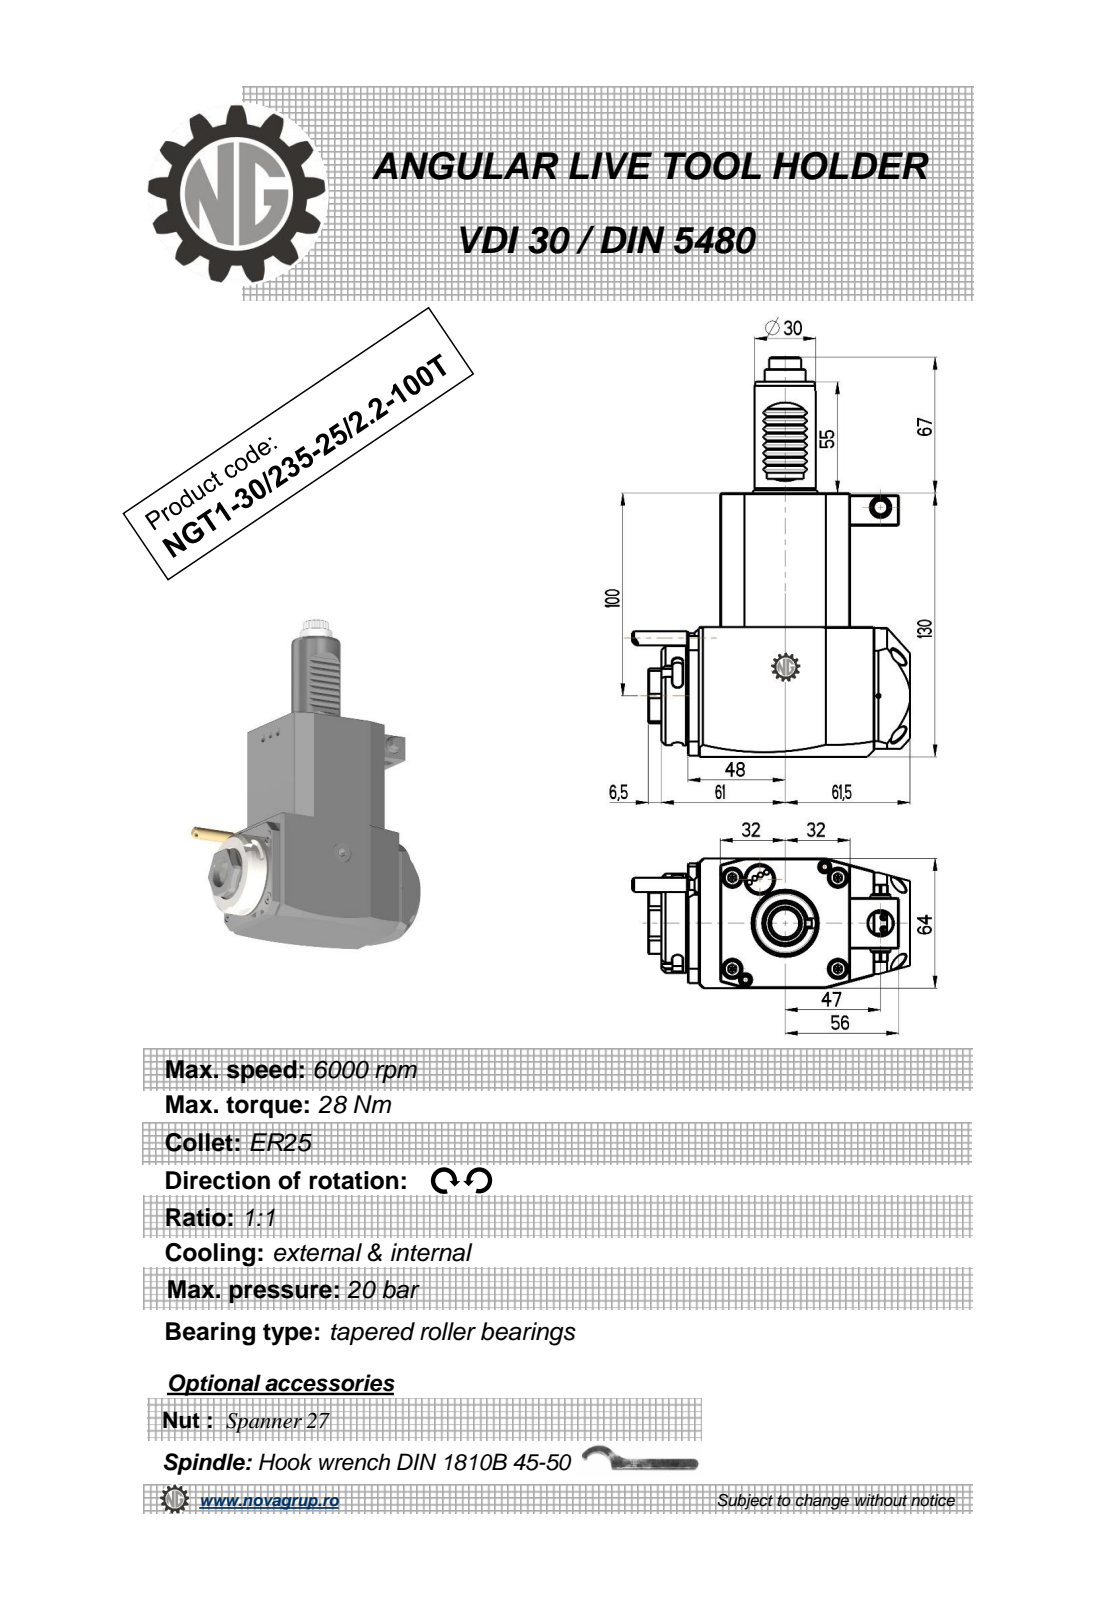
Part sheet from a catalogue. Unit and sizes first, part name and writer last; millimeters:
Units: millimetres
Overall size (bounding box): 197 × 136.88 × 64
Round holes (diameter × count): ⌀2.5 ×1, ⌀3 ×1, ⌀9.5 ×1, ⌀12 ×1, ⌀18 ×1
Round bosses / shafts (diameter × count): ⌀8 ×2, ⌀49 ×1, ⌀42 ×1, ⌀30 ×1, ⌀20 ×1, ⌀10 ×1, ⌀7 ×1, ⌀5 ×1
Partial cylindrical surfaces — rounded edges, fillets, slot ends (radius × count): R1.98 ×36, R0.3 ×8, R2.5 ×6, R180 ×2, R3.85 ×1, R4.25 ×1, R4.5 ×1, R7.08 ×1
Main face-to-face distances: 64, 130, 16, 80, 72.18, 13, 29.5, 93.5, 109.5, 66
Hole centre spacings: 34.25, 65.8, 91.5
Volume: 739 925 mm³ · Surface area: 62 056 mm²
Bodies: 1 solid, 427 faces (186 planar, 153 cylindrical, 88 other)
Part name (STEP PRODUCT): NGT1_30_235_25_1_2_100T
STEP written by: PRO/ENGINEER BY PARAMETRIC TECHNOLOGY CORPORATION, 2010280 (CONFIG_CONTROL_DESIGN)
